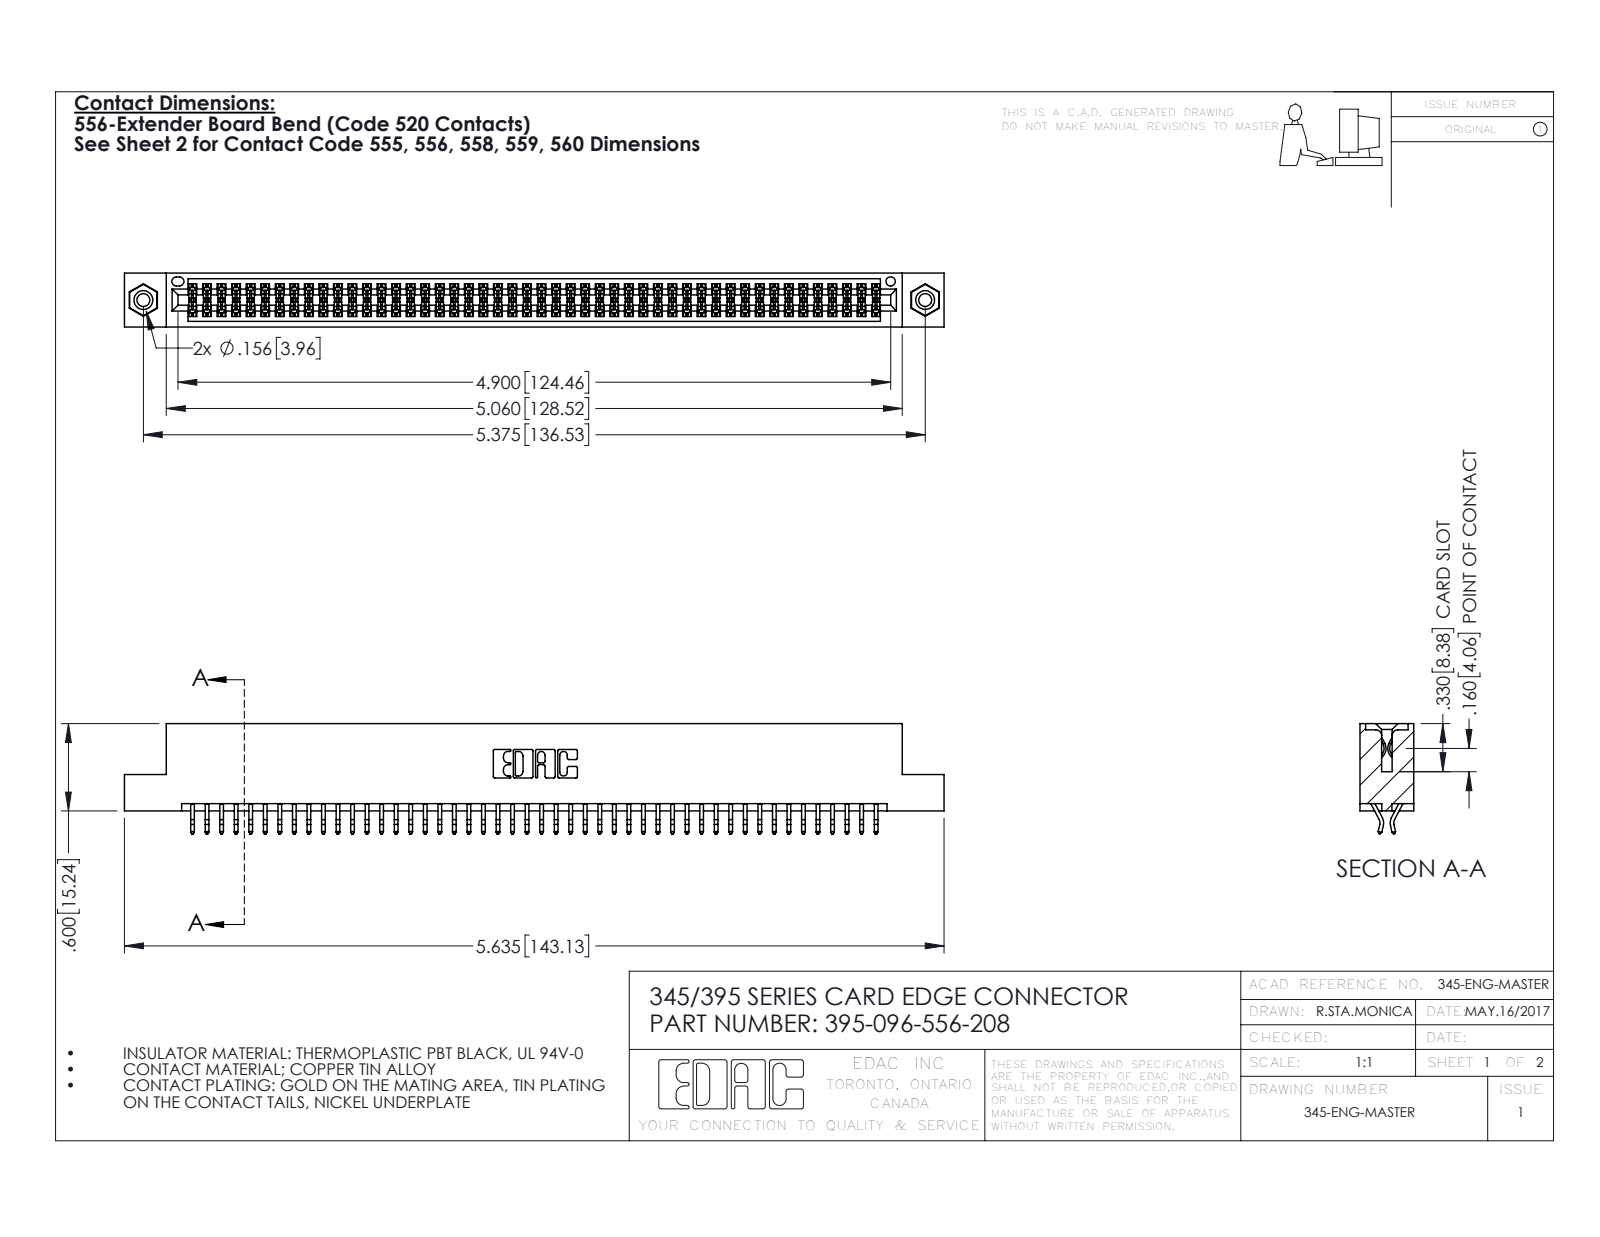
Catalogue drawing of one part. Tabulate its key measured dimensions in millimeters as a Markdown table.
| quantity | value |
| --- | --- |
| part name | 395-096-556-208; 345-292-001_556 Tail; 345-250-001_345-250-003-102; 345 Part_Flush Mounting Lugs - 0.156 Dia-TI |
| STEP written by | SolidWorks 2016 (CONFIG_CONTROL_DESIGN) |
| units | millimeters |
| bodies | 99 solids, 5562 faces (3664 planar, 1882 cylindrical, 16 other) |
| overall size | 143.1 × 19.2 × 9.4 |
| volume | 13 900 mm³ |
| surface area | 20 660 mm² |
| round holes (diameter × count) | 2.3 × 2, 3.2 × 2, 4 × 2, 1.6 × 1 |
| round bosses / shafts (diameter × count) | 3.9 × 2 |
| partial cylindrical surfaces (radius × count) | 0.2 × 144, 0.3 × 22, 0.2 × 6, 0.8 × 6, 0.7 × 3, 0.3 × 2, 0.4 × 2, 0.5 × 2 |
| main face-to-face distances | 1.8, 7.6, 9.4, 5.1, 0.6, 2.5, 6.9, 5.7, 4.4, 3.8 |
| hole center spacings | 6.9, 130.5, 136.5 |
